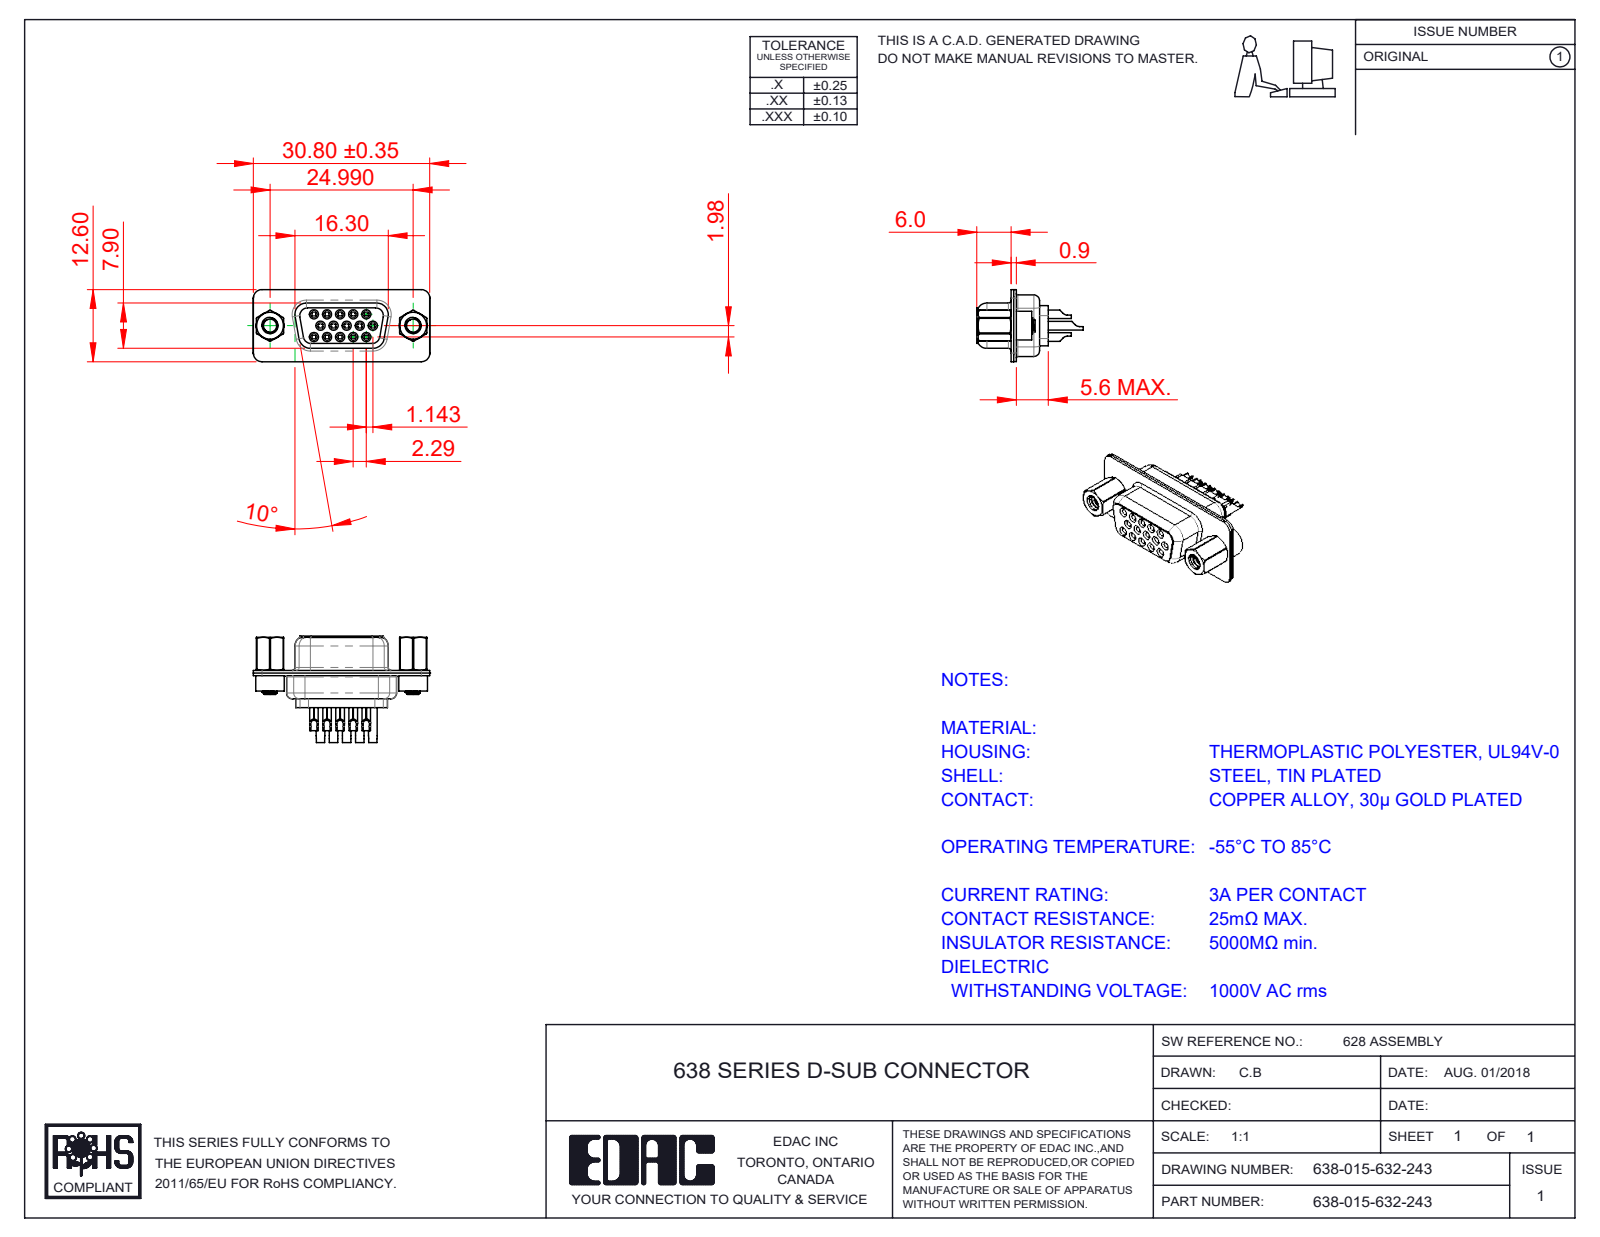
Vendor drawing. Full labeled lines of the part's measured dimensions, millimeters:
Part name (STEP PRODUCT): 638 4-40 Threaded Rivet; 638 4-40 Hex Standoff; 638 Shell Rear_15 Contacts; 638 Housing_15 Contacts (+5 more)
STEP written by: SolidWorks 2020 (CONFIG_CONTROL_DESIGN)
Units: millimetres
Bodies: 22 solids, 1740 faces (404 planar, 584 cylindrical, 752 other)
Overall size (bounding box): 30.81 × 18.6 × 12.6
Volume: 1 816 mm³ · Surface area: 6 344 mm²
Round holes (diameter × count): ⌀0.8 ×15, ⌀1 ×15, ⌀1.1 ×15, ⌀1.6 ×15, ⌀1.7 ×15, ⌀1.8 ×15, ⌀2 ×2, ⌀2.26 ×2, ⌀2.29 ×2, ⌀4 ×2, ⌀4.05 ×2, ⌀4.85 ×2
Round bosses / shafts (diameter × count): ⌀2 ×15, ⌀1.5 ×15, ⌀1.2 ×15, ⌀5 ×2, ⌀4.95 ×2, ⌀4.8 ×2, ⌀2.79 ×2
Partial cylindrical surfaces — rounded edges, fillets, slot ends (radius × count): R1.5 ×20, R2 ×12, R0.28 ×10, R1.55 ×8, R1 ×7, R1.35 ×5, R0.25 ×4, R0.5 ×4
Main face-to-face distances: 0.45, 0.9, 0.4, 1.43, 8.88, 6.6, 1.4, 2.28, 6.2, 0.85
Hole centre spacings: 3.96, 2.28, 4.57, 2.29, 6.05, 6.04, 6.86, 7.92
